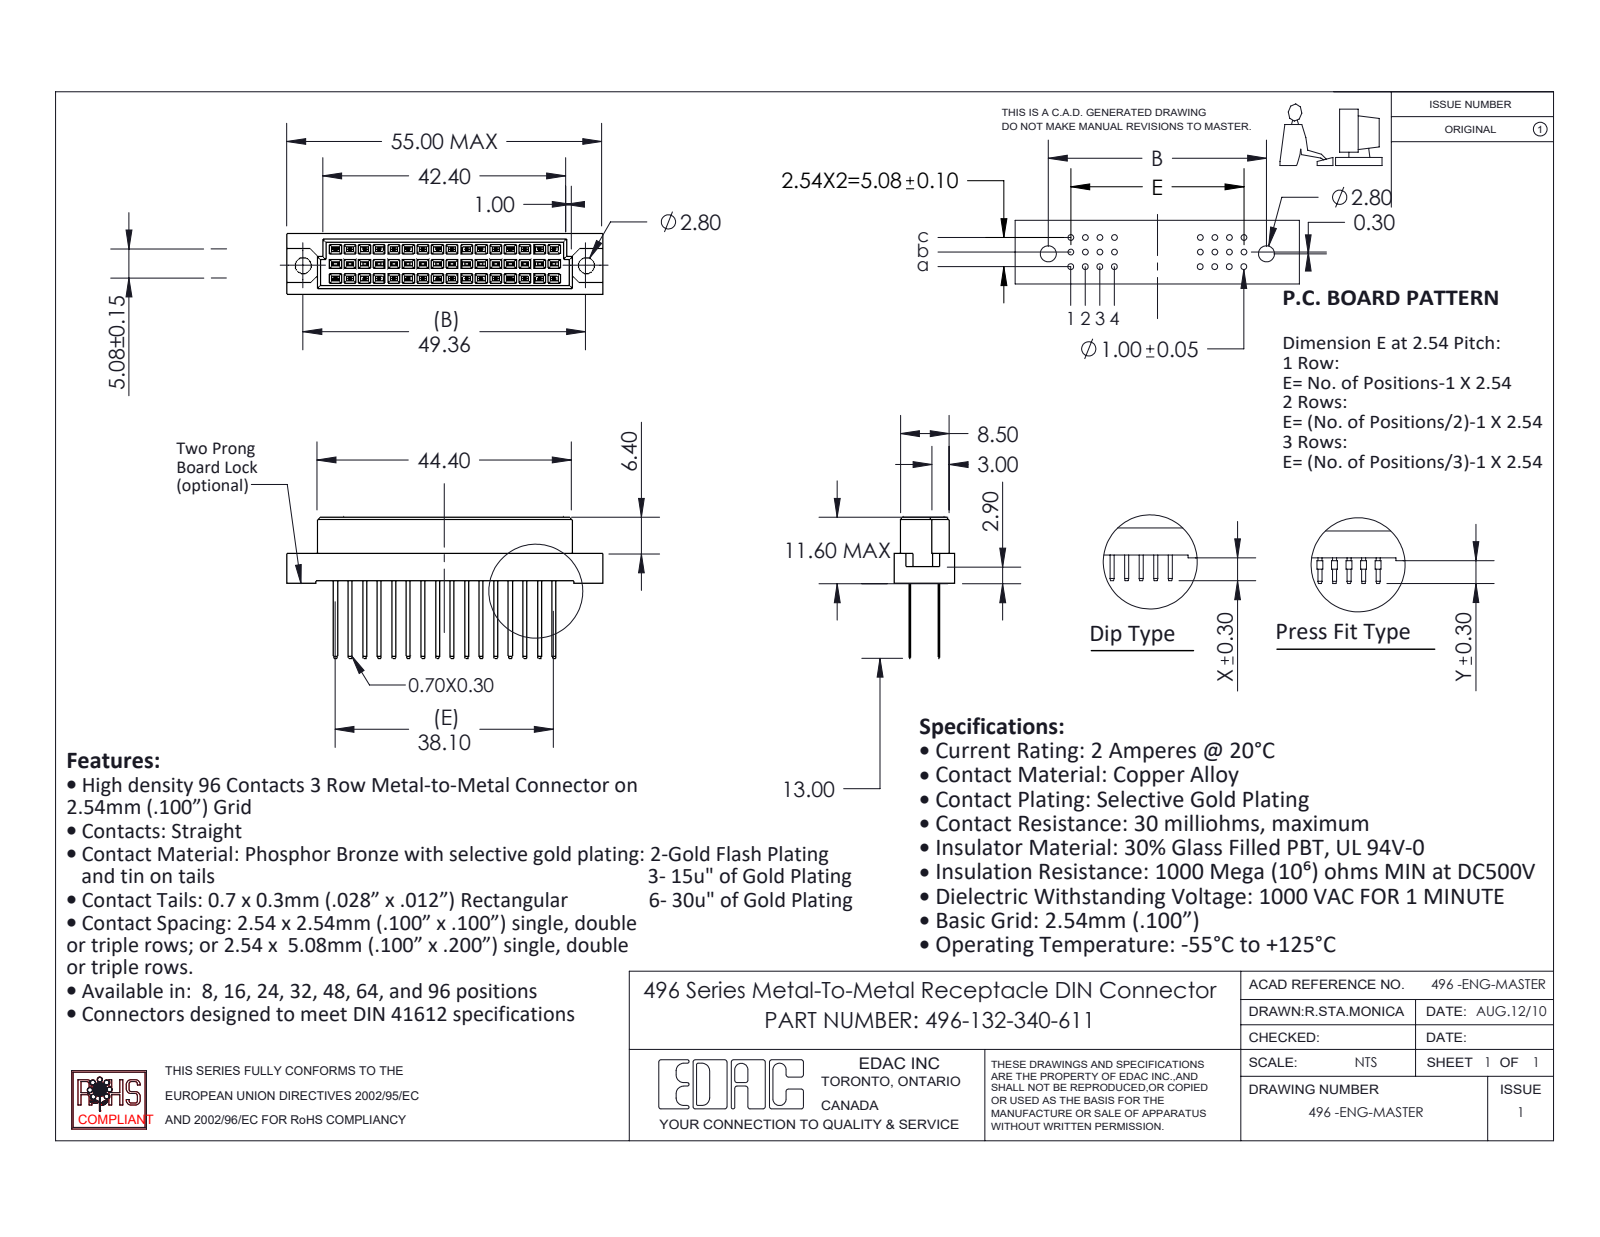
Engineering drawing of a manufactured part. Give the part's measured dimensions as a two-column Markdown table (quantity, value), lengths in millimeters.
| quantity | value |
| --- | --- |
| part name | 496-290_40; 496 Part_48; 496-132-340-611 |
| STEP written by | SolidWorks 2020 (CONFIG_CONTROL_DESIGN) |
| units | millimeters |
| bodies | 33 solids, 986 faces (982 planar, 4 cylindrical, 0 other) |
| overall size | 55 × 24.6 × 10.6 |
| volume | 4 705 mm³ |
| surface area | 5 324 mm² |
| round holes (diameter × count) | 2.8 × 2 |
| main face-to-face distances | 5.08, 2.54, 1.05, 9.55, 2.61, 2.91, 7.69, 7.99, 1.56, 1.86 |
| hole center spacings | 49.36 |
